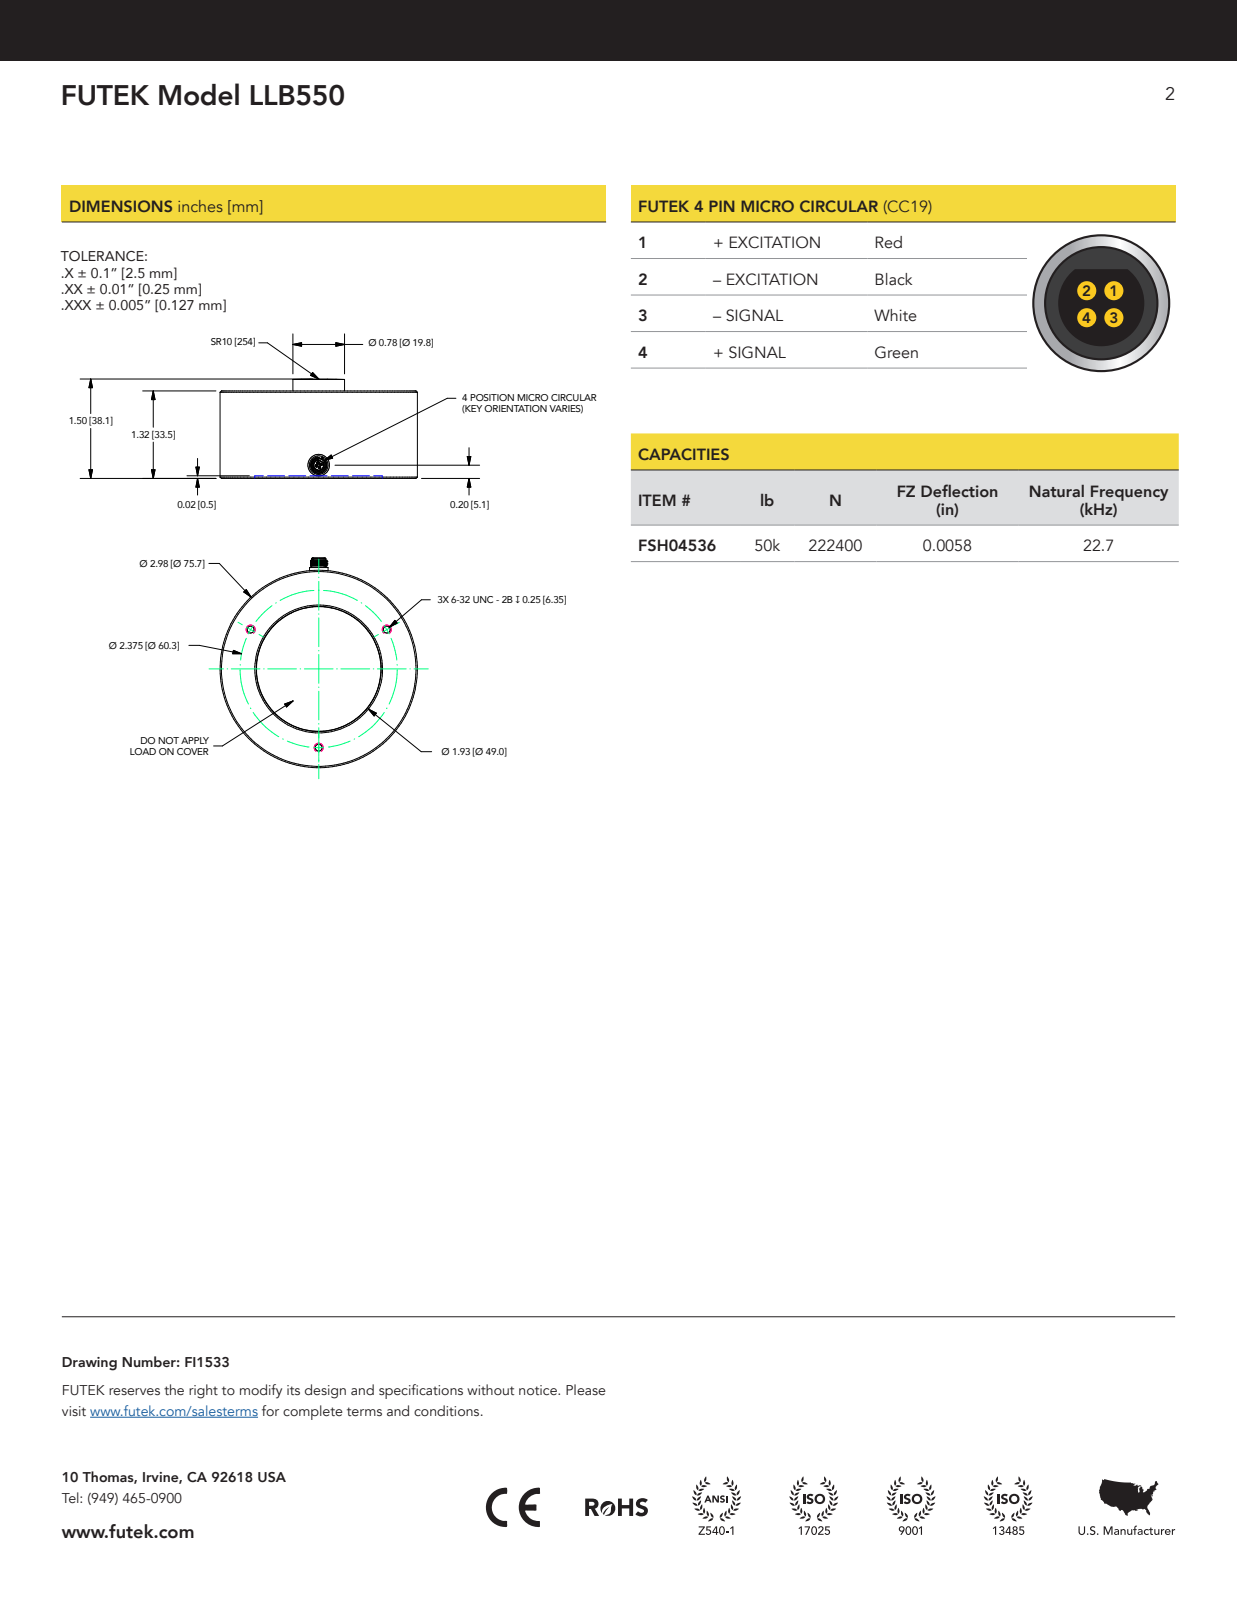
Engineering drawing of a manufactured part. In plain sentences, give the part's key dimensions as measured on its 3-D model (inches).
The part is named "LLB550 (LevelofDetail1); ~~~~PART1; 778C; 778CA (+1 more)". Its 3-D file was written by "Autodesk Inventor 2008 (AUTOMOTIVE_DESIGN)". It is 3 solids with 118 faces: 23 planar, 17 cylindrical and 78 other. Overall it measures 6.619 by 2.98 by 1.5 inches. Its volume is 9.247 cubic inches and its surface area 30.73 square inches. Round holes: 3 of diameter 0.109, 1 of diameter 0.13, 1 of diameter 0.155, 1 of diameter 0.189, 1 of diameter 0.21, 1 of diameter 0.219, 1 of diameter 0.228, 1 of diameter 1.77, 1 of diameter 1.83. Round bosses or shafts: 3 of diameter 0.125, 1 of diameter 2.98, 1 of diameter 0.78, 1 of diameter 0.278. The main face-to-face distances are 1.32, 1.31, 1.3, 1.29, 0.02, 0.307, 0.297, 0.993, 1.013, 0.073. The hole center spacings are 1.187, 2.057.
